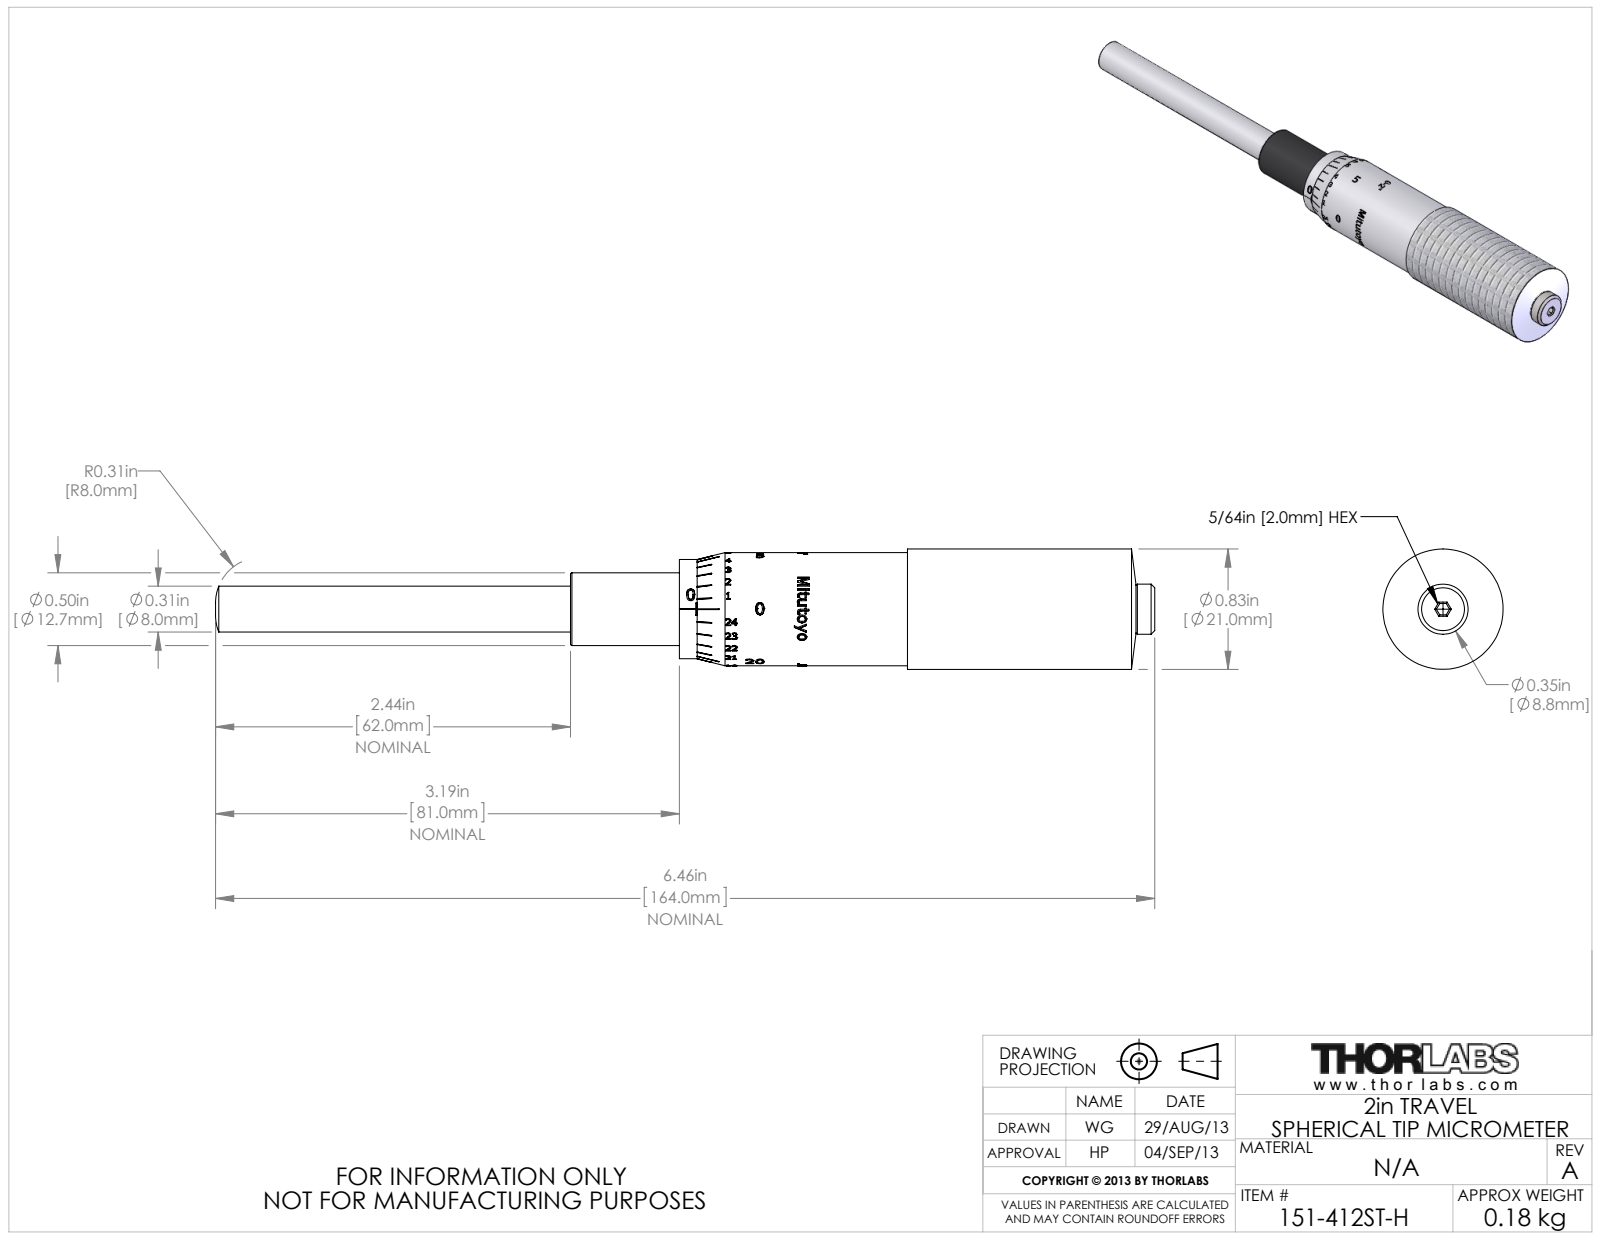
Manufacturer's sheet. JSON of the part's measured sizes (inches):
{"part_name": "TTN017746-E0W", "step_written_by": "SolidWorks 2012 (AUTOMOTIVE_DESIGN)", "units": "inches", "bodies": {"solids": 2, "faces": 1069, "planar": 475, "cylindrical": 116, "other": 478}, "overall_size": [6.458, 0.827, 0.827], "volume_in3": 1.904, "surface_area_in2": 12.94, "round_holes": [[0.157, 1]], "round_bosses_or_shafts": [[0.827, 1], [0.778, 1], [0.682, 1], [0.499, 1], [0.345, 1], [0.315, 1], [0.137, 1]], "partial_cylinders_radius": [[0.375, 10], [0.34, 1], [0.366, 1], [0.389, 1]], "face_to_face_distances": [3.138, 3.887, 0.749, 1.571, 1.567, 2.316, 0.13, 1.701, 3.268, 4.017]}
